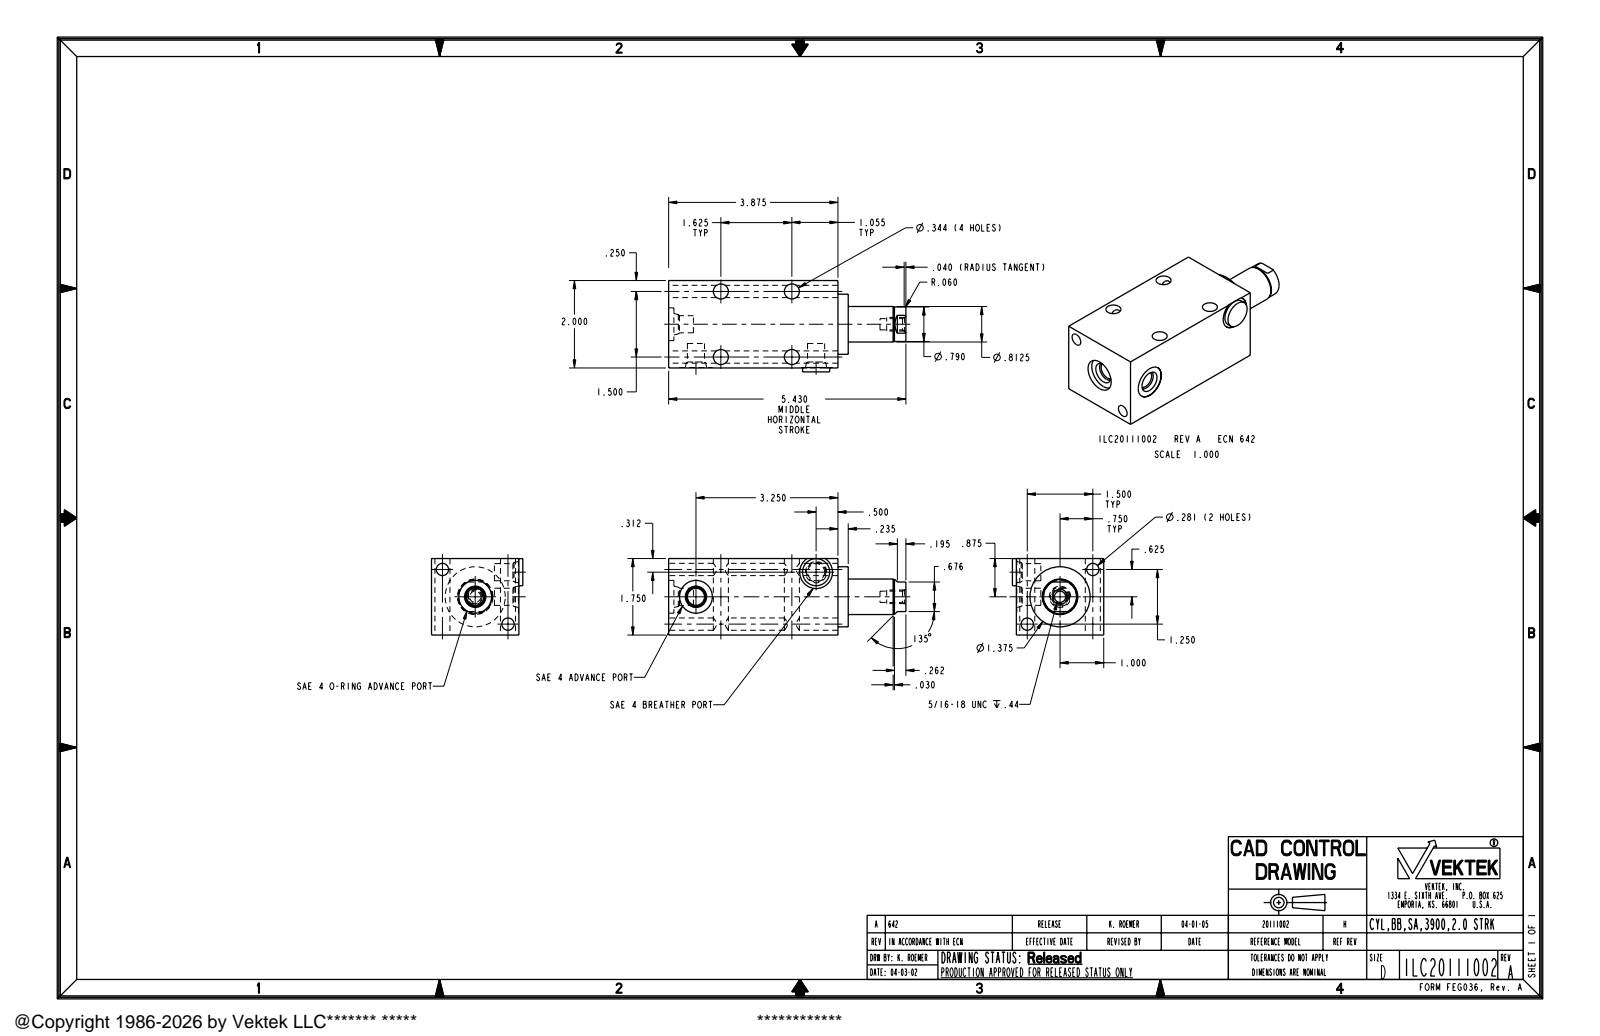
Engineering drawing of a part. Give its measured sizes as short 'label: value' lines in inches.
name: ILC20111002
written by: PRO/ENGINEER BY PARAMETRIC TECHNOLOGY CORPORATION, 2004290 (AUTOMOTIVE_DESIGN_CC2)
unit: in
bodies: 1 solid, 83 faces (22 planar, 43 cylindrical, 18 other)
size: 5.43 × 2.09 × 1.75
volume: 13.26 in³; area: 55.85 in²
holes: 4× ⌀0.344, 3× ⌀0.392, 3× ⌀0.75, 2× ⌀0.281, 1× ⌀0.257
bosses: 1× ⌀1.375, 1× ⌀0.813, 1× ⌀0.79, 1× ⌀0.62, 1× ⌀0.312
face distances: 1.75, 2, 3.875, 0.235, 4.11, 1.99, 1.32, 1.555, 5.43, 0.09
hole spacings: 0.976, 1.5, 1.625, 2.211, 1.953, 2.807
